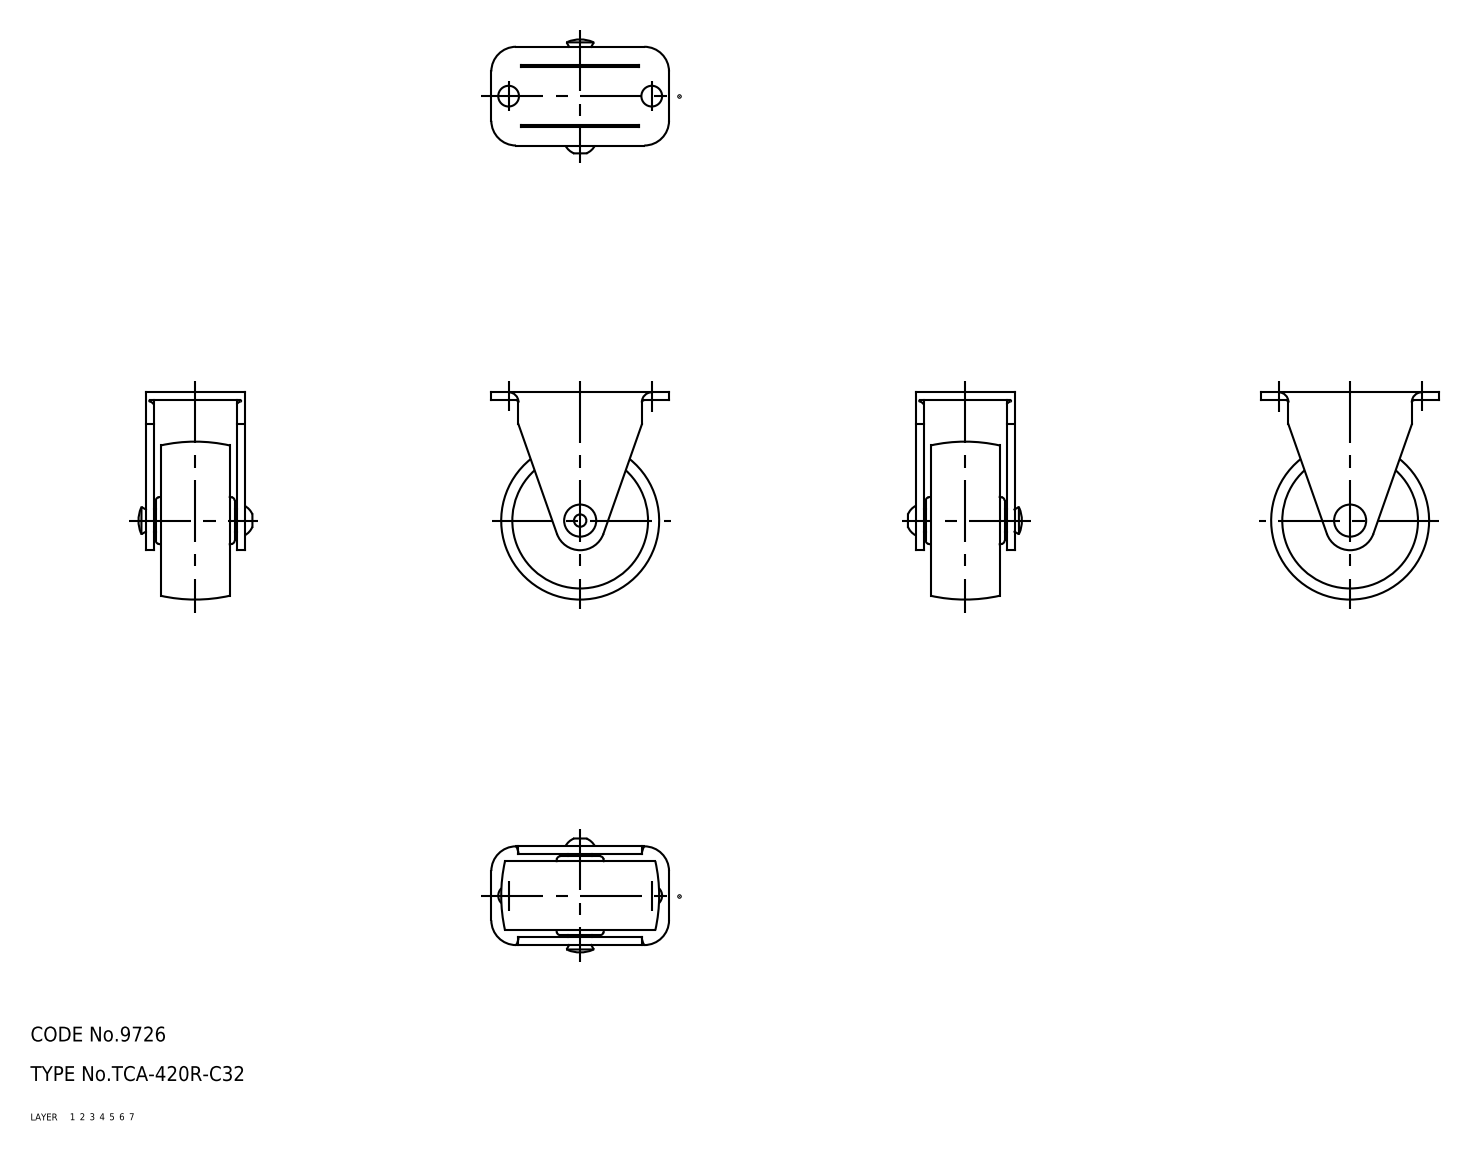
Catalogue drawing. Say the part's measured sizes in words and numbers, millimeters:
The part is named "wheel; axle; No_420_R_C32_2_32756_36". Its 3-D file was written by "CADfix (AUTOMOTIVE_DESIGN)". It is 3 solids with 89 faces: 0 planar, 0 cylindrical and 89 other. Overall it measures 42 by 36 by 23.09 millimeters. Its volume is 11 303 cubic millimeters and its surface area 7 729 square millimeters.
